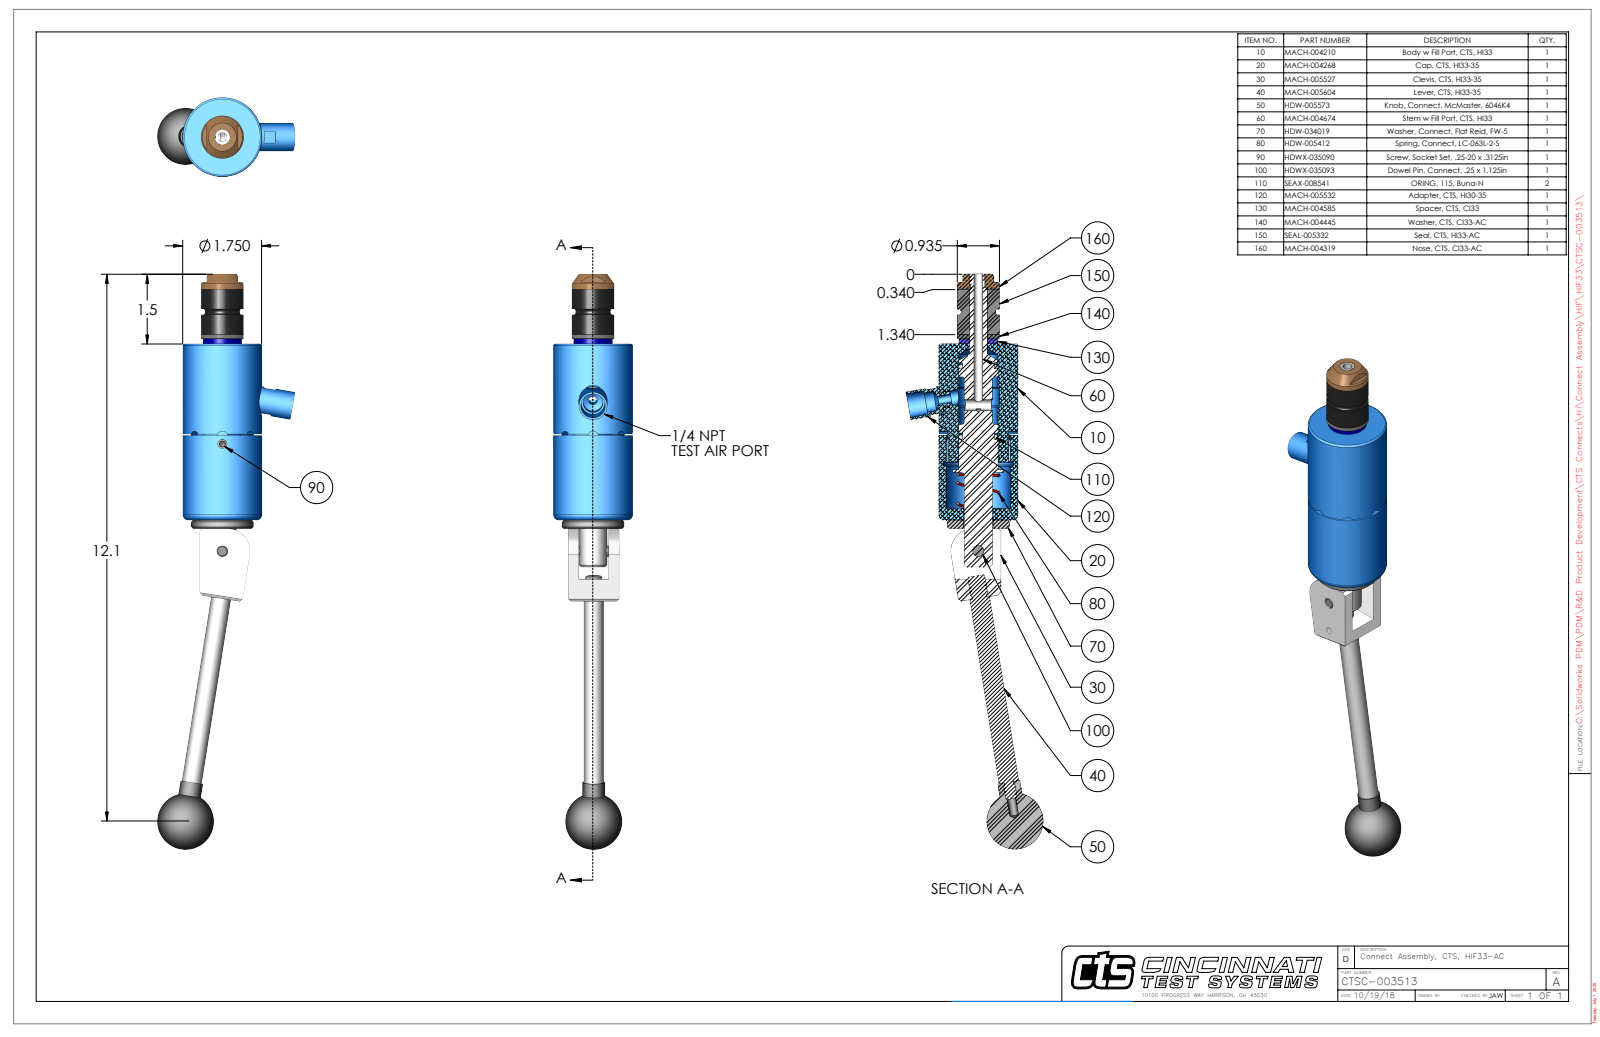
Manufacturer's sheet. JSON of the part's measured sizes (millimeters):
{"part_name": "CTSC-003513", "step_written_by": "SolidWorks 2023 (AUTOMOTIVE_DESIGN)", "units": "millimeters", "bodies": {"solids": 10, "faces": 281, "planar": 90, "cylindrical": 125, "other": 66}, "overall_size": [323.9, 77.3, 44.5], "volume_mm3": 221700, "surface_area_mm2": 48390, "round_holes": [[5.1, 2], [8, 2], [3.8, 1], [4.7, 1], [5.2, 1], [6.3, 1], [6.4, 1], [6.4, 1], [9.9, 1], [10.1, 1], [10.2, 1], [11.1, 1]], "round_bosses_or_shafts": [[9.5, 2], [7.9, 2], [6.4, 2], [44.5, 1], [35.1, 1], [23.7, 1], [21.8, 1], [15.9, 1]], "partial_cylinders_radius": [[3.2, 4], [0.7, 2], [3.6, 1], [4.2, 1], [4.2, 1], [8.4, 1], [12.7, 1], [17.7, 1]], "face_to_face_distances": [99.2, 28.4, 104, 4.8, 30.7, 129.9, 134.7, 22.6, 5.9, 5.9], "hole_center_spacings": [18.8, 60.4, 79.1]}
